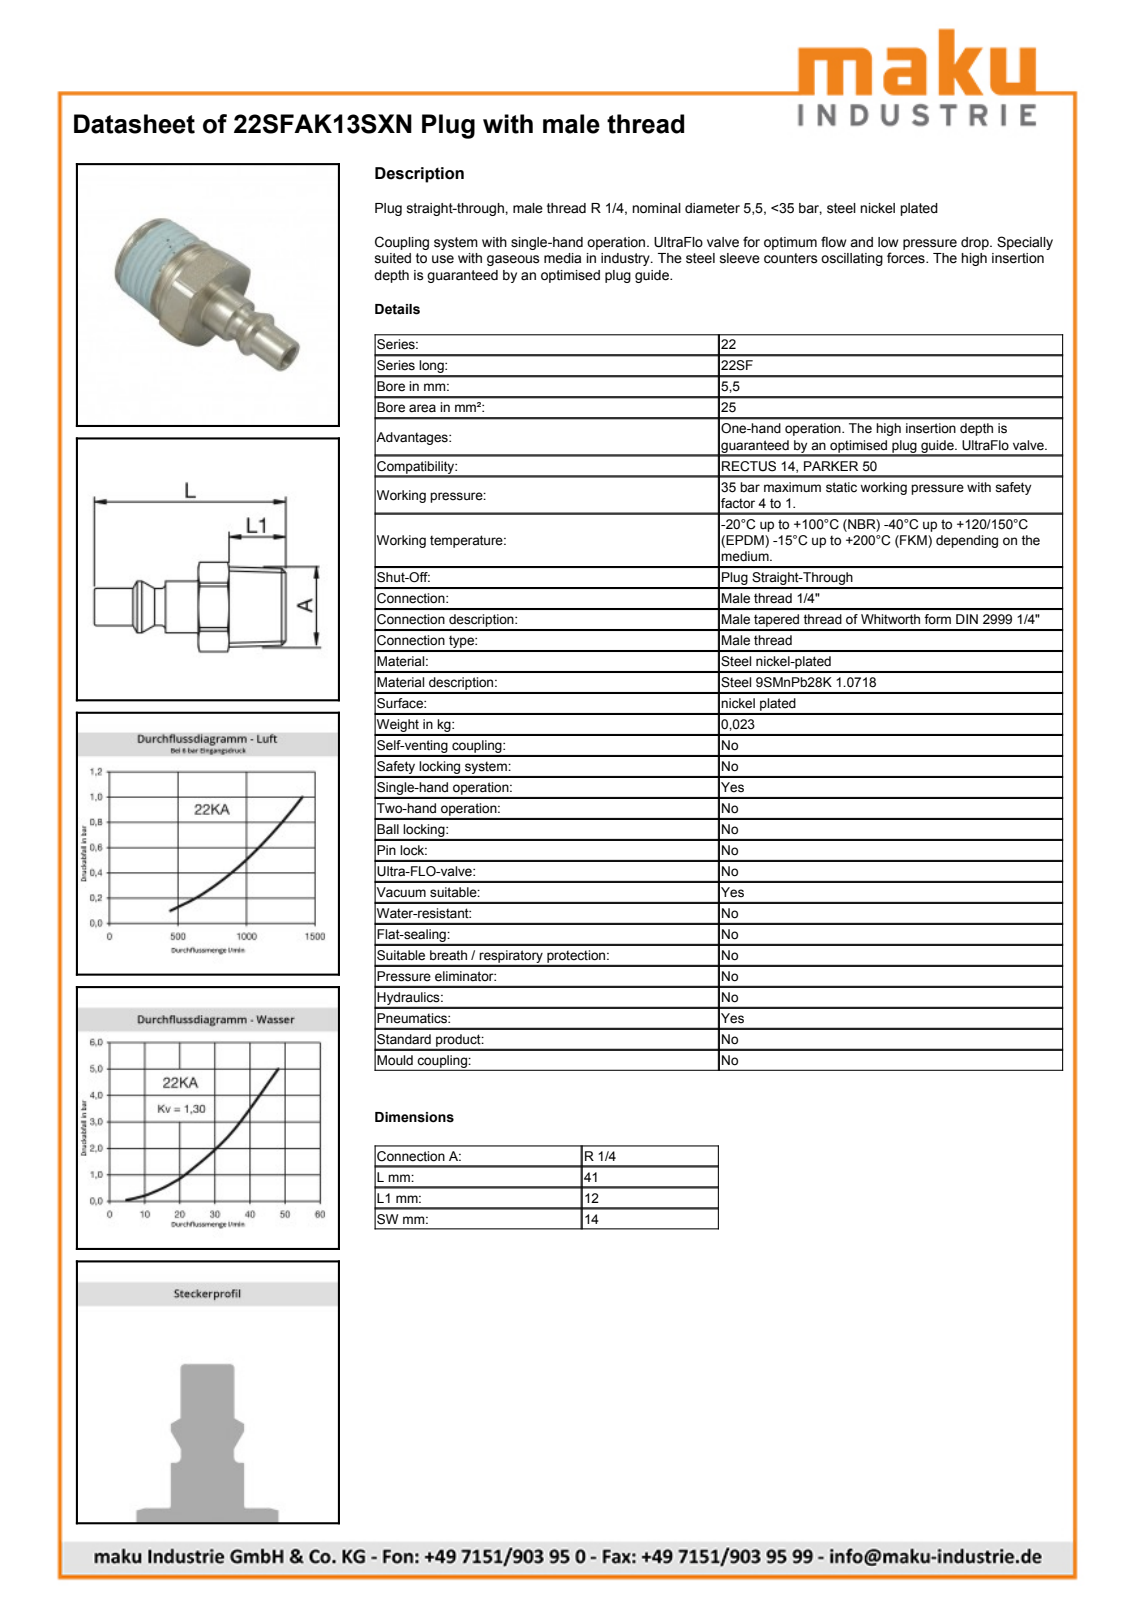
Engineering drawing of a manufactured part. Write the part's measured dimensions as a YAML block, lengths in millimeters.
part_name: "D108993"
step_written_by: "Autodesk Inventor 2013 (AUTOMOTIVE_DESIGN)"
units: millimeters
bodies: {solids: 1, faces: 44, planar: 11, cylindrical: 12, other: 21}
overall_size: [40.5, 15.8, 14]
volume: 2811
surface_area: 2519
round_holes:
  - {diameter: 5.5, count: 1}
  - {diameter: 7.5, count: 1}
round_bosses_or_shafts:
  - {diameter: 10.9, count: 1}
  - {diameter: 7.9, count: 1}
  - {diameter: 7.8, count: 1}
partial_cylinders:
  - {radius: 7.9, count: 1}
face_to_face_distances: [14, 18.5, 6.93, 25.43, 15.07, 22, 40.5, 28.5, 13.43, 6.5]
